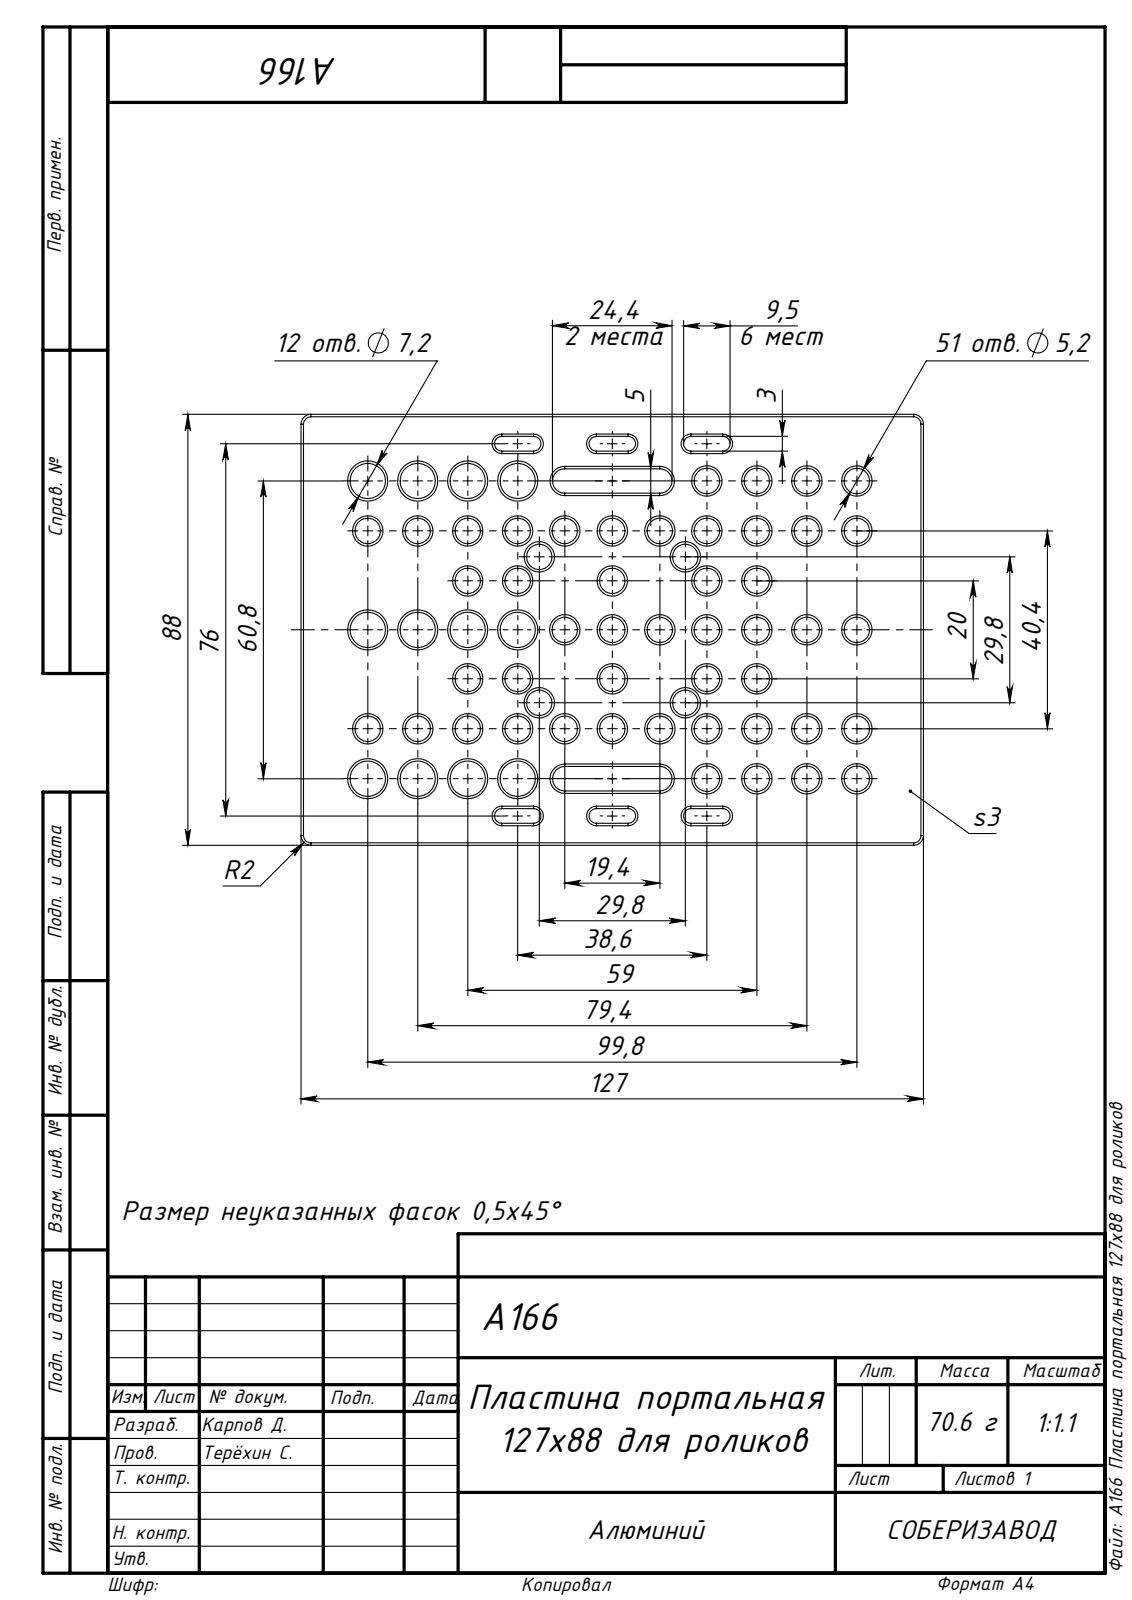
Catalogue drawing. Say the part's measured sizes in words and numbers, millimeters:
The part is named "A166 Пластина портальная 127х88 для роликов". Its 3-D file was written by "SolidWorks 2018 (AUTOMOTIVE_DESIGN)". It is 1 solid with 519 faces: 60 planar, 154 cylindrical and 305 other. Overall it measures 127 by 88 by 3 millimeters. Its volume is 27 170 cubic millimeters and its surface area 22 762 square millimeters. Round holes: 51 of diameter 5.2, 12 of diameter 7.2. Partial cylindrical surfaces (rounded edges, fillets, slot ends): 12 of radius 1.5, 4 of radius 2, 4 of radius 2.5. The main face-to-face distances are 3, 88, 63.63, 127, 91.21, 11.1, 16.1, 71.9, 76.9, 5. The hole center spacings are 10.2, 14.42, 22.81, 20.2, 22.41, 9.7, 20.4, 21.83.
